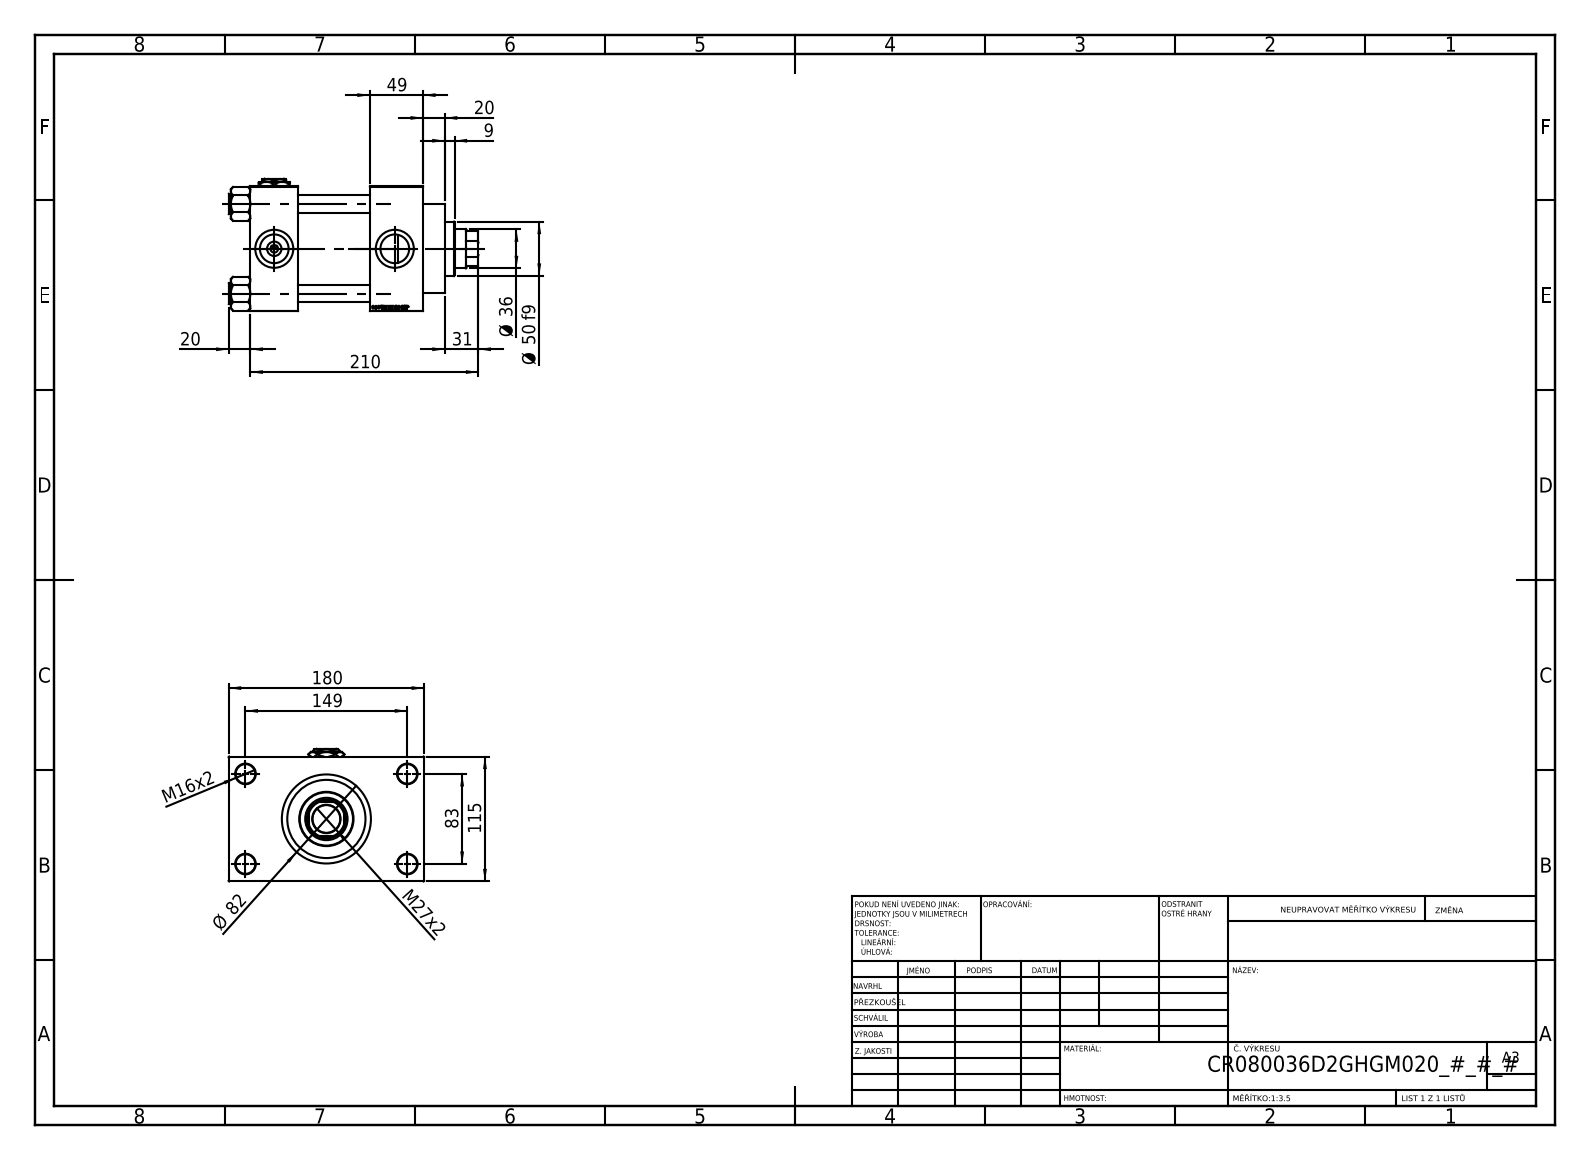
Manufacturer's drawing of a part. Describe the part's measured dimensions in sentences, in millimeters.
The part is named "V215_VC_A; V215CR_D_Body; NUT_M5_D; Zatka_pro_OIL_PORT (+2 more)". Its 3-D file was written by "SolidWorks 2019 (CONFIG_CONTROL_DESIGN)". It is 12 solids with 1204 faces: 569 planar, 95 cylindrical and 540 other. Overall it measures 230 by 180 by 122 millimeters. Its volume is 1 976 000 cubic millimeters and its surface area 300 381 square millimeters. Round holes: 4 of diameter 16, 4 of diameter 18, 3 of diameter 7, 3 of diameter 26.44, 3 of diameter 35, 1 of diameter 25.5, 1 of diameter 36, 1 of diameter 39, 1 of diameter 61, 1 of diameter 72, 1 of diameter 80. Round bosses or shafts: 4 of diameter 19, 1 of diameter 86, 1 of diameter 82, 1 of diameter 50. Partial cylindrical surfaces (rounded edges, fillets, slot ends): 1 of radius 17.5. The main face-to-face distances are 115, 66, 110, 49, 44, 159, 32.5, 147.5, 20, 69. The hole center spacings are 33.15, 58.48, 82.7, 85.28, 89.24, 115.85, 142.43, 83.
